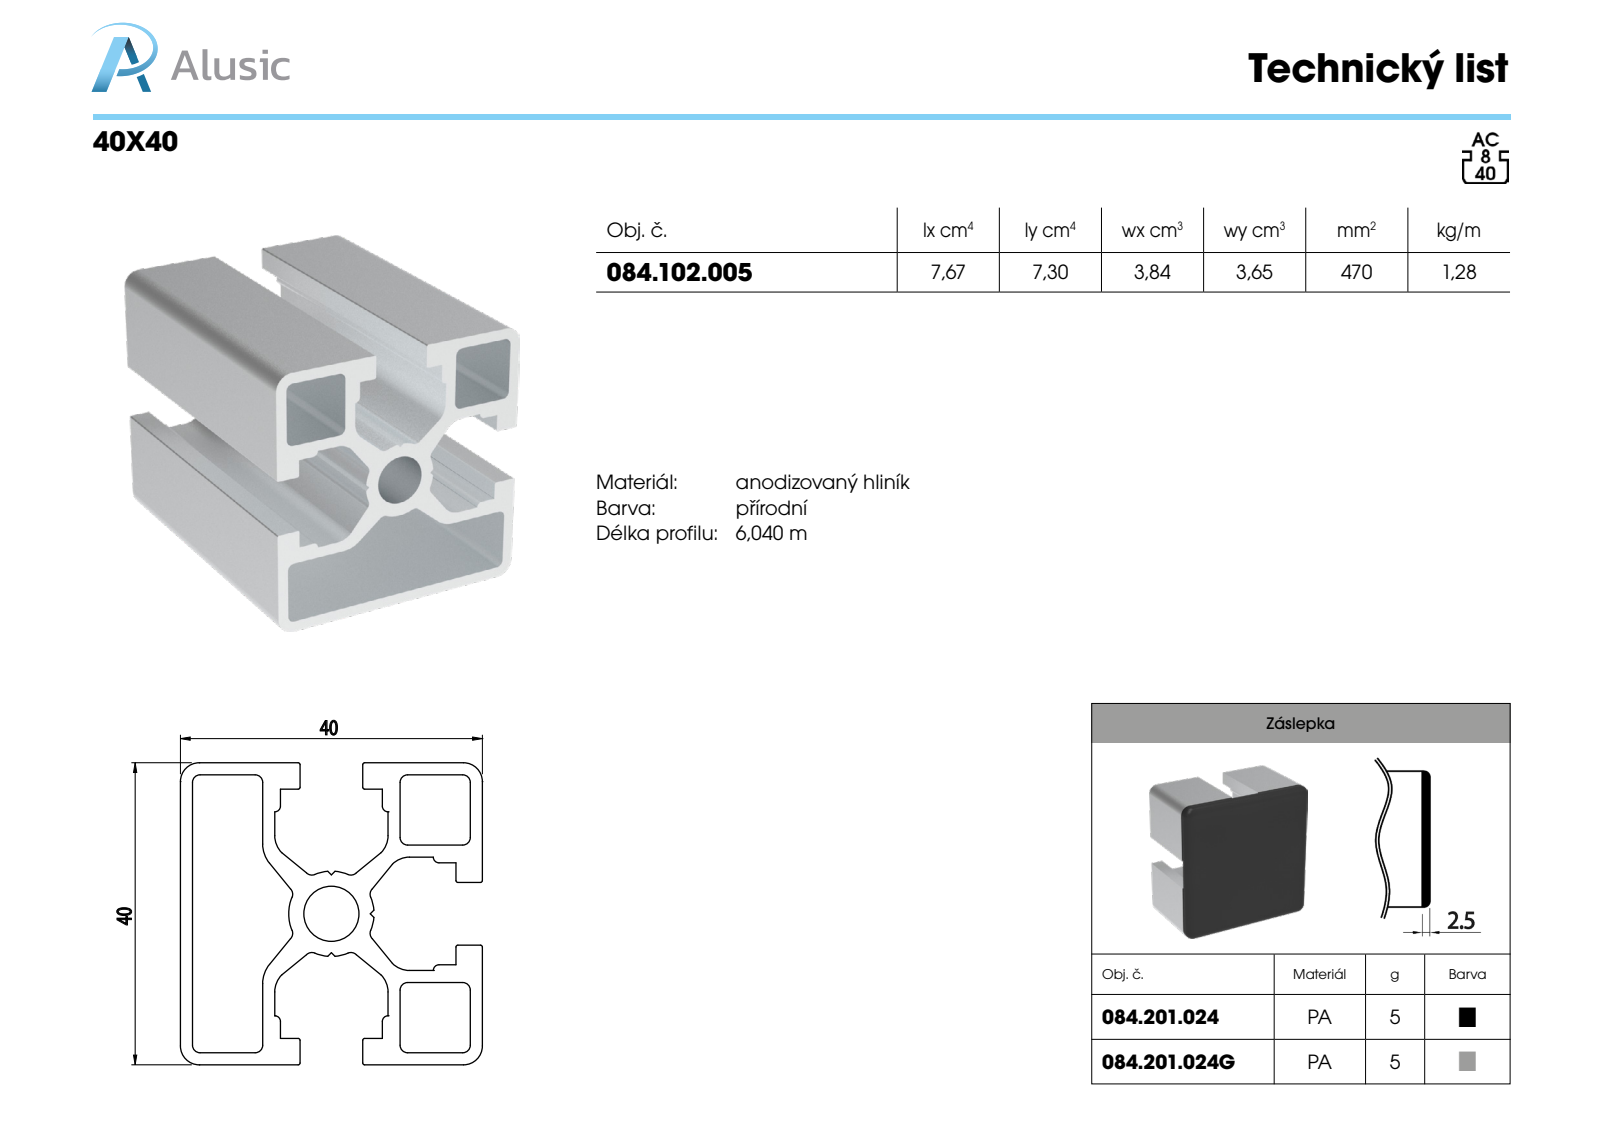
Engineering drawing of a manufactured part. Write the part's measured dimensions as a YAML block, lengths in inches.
part_name: "084.102.005"
step_written_by: "SolidWorks 2011 (CONFIG_CONTROL_DESIGN)"
units: inches
bodies: {solids: 1, faces: 121, planar: 60, cylindrical: 61, other: 0}
overall_size: [3.937, 1.575, 1.575]
volume: 2.864
surface_area: 71.97
round_holes:
  - {diameter: 0.287, count: 1}
partial_cylinders:
  - {radius: 0.039, count: 20}
  - {radius: 0.01, count: 12}
  - {radius: 0.03, count: 6}
  - {radius: 0.126, count: 6}
  - {radius: 0.098, count: 4}
  - {radius: 0.157, count: 2}
  - {radius: 0.222, count: 1}
face_to_face_distances: [0.063, 0.429, 1.512, 1.083, 1.575, 1.146, 0.366, 0.522, 0.624, 0.459]
